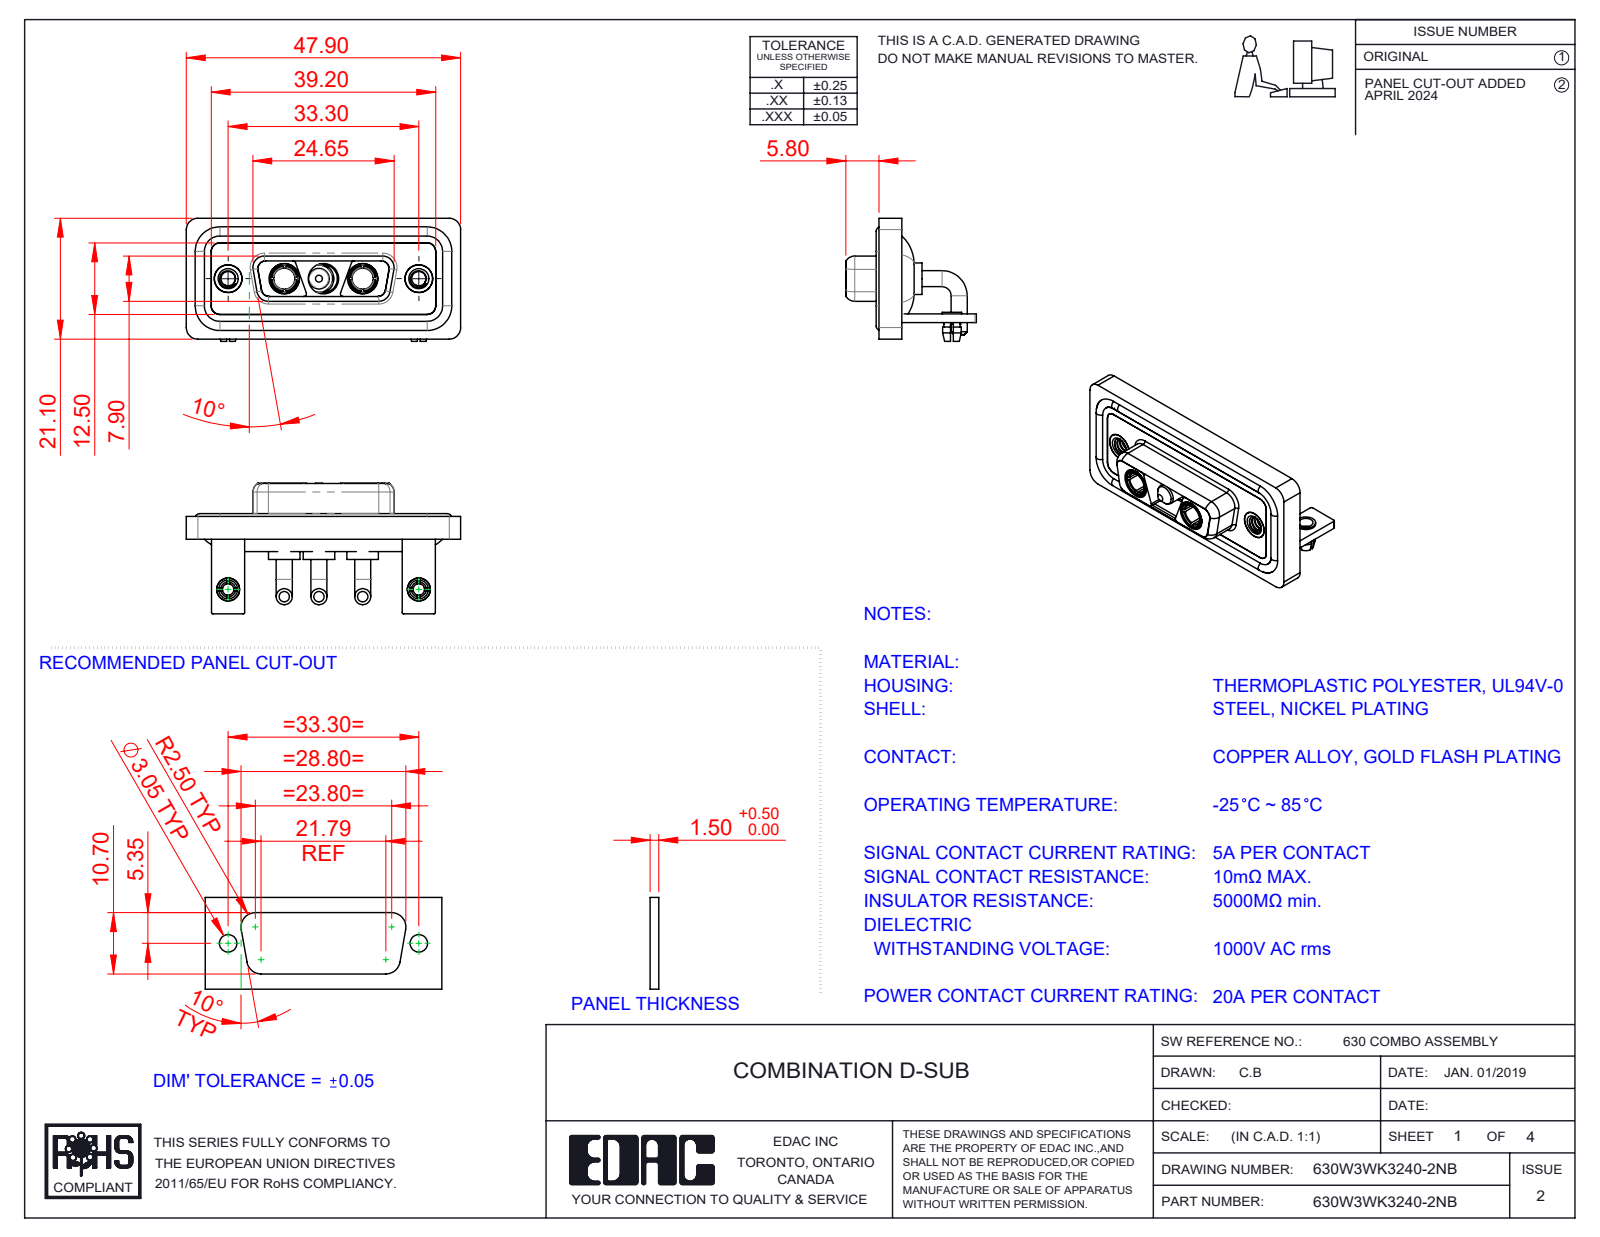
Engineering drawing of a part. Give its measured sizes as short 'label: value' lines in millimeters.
name: 630Combo Shell Rear_15 Contacts; 630W3WK3240-2NB; 630Combo Waterproof Housing_15 Contacts; 630Combo Board Lock_50 Contacts (+6 more)
written by: SolidWorks 2023 (CONFIG_CONTROL_DESIGN)
unit: mm
bodies: 17 solids, 729 faces (246 planar, 318 cylindrical, 165 other)
size: 47.9 × 22.8 × 21.5
volume: 6 427 mm³; area: 10 687 mm²
holes: 5× ⌀4.85, 4× ⌀2.5, 3× ⌀5.3, 2× ⌀2, 2× ⌀3.2, 2× ⌀3.7, 2× ⌀4, 2× ⌀4.05, 2× ⌀5
bosses: 6× ⌀2.8, 4× ⌀1.6, 3× ⌀5.5, 3× ⌀5.2, 3× ⌀4.75, 3× ⌀3.75, 2× ⌀4.96, 2× ⌀4.95
rounds: 21× R2, 18× R1.5, 16× R0.25, 12× R1.35, 9× R0.5, 8× R1.6, 4× R0.6, 4× R0.65
face distances: 0.4, 2.9, 1.5, 3.7, 1.8, 1.1, 4.1, 1.6, 2.5, 1.4
hole spacings: 6.85, 9.8, 16.65, 23.5, 33.3, 13.7
